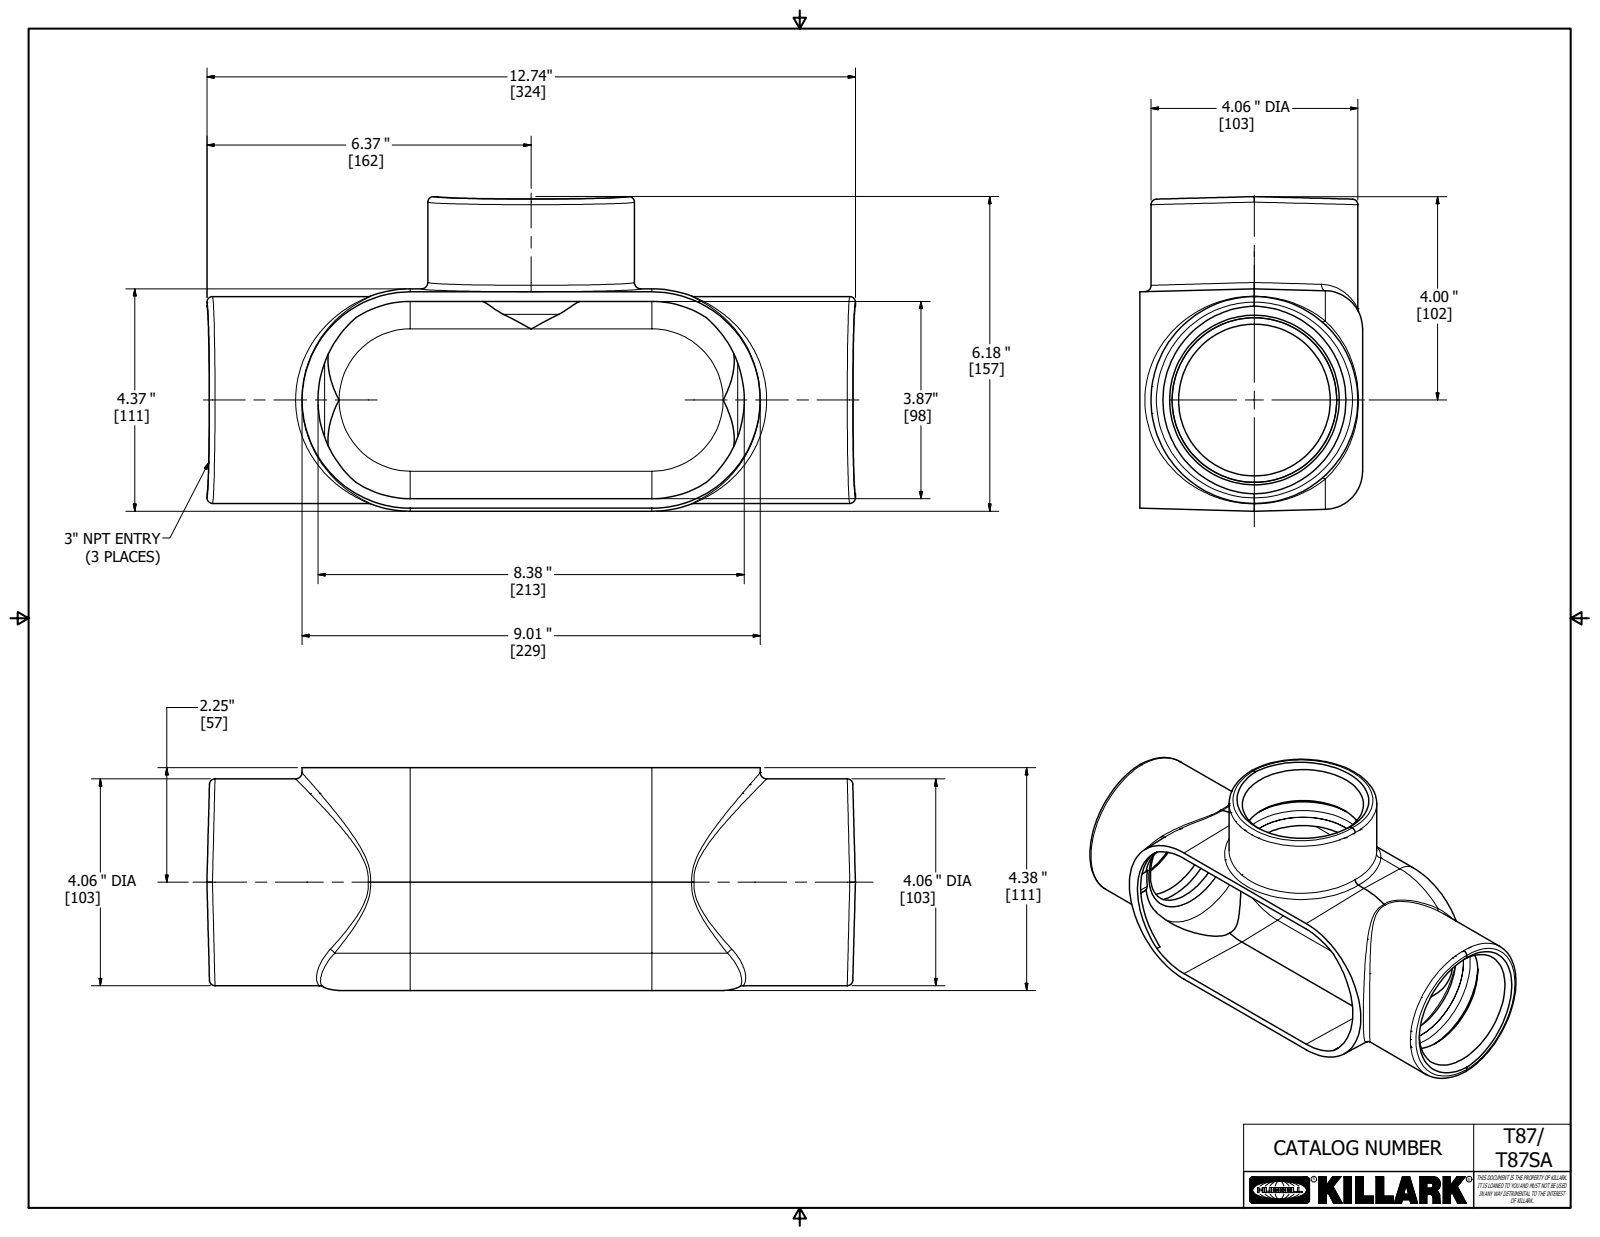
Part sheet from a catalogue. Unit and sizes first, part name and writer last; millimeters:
Units: millimetres
Overall size (bounding box): 323.7 × 157 × 111.1
Round holes (diameter × count): ⌀89.2 ×2, ⌀98.4 ×1
Round bosses / shafts (diameter × count): ⌀103.2 ×2
Partial cylindrical surfaces — rounded edges, fillets, slot ends (radius × count): R1.3 ×4, R3.2 ×4, R14.3 ×2, R19.1 ×2, R49.2 ×1
Main face-to-face distances: 4.7, 106.2, 101.4, 111.1, 106.3, 110.9, 0.8, 4, 110.3, 50.8
Volume: 693 000 mm³ · Surface area: 229 400 mm²
Bodies: 1 solid, 118 faces (38 planar, 22 cylindrical, 58 other)
Part name (STEP PRODUCT): 17731
STEP written by: Autodesk Inventor 2018 (AUTOMOTIVE_DESIGN)
